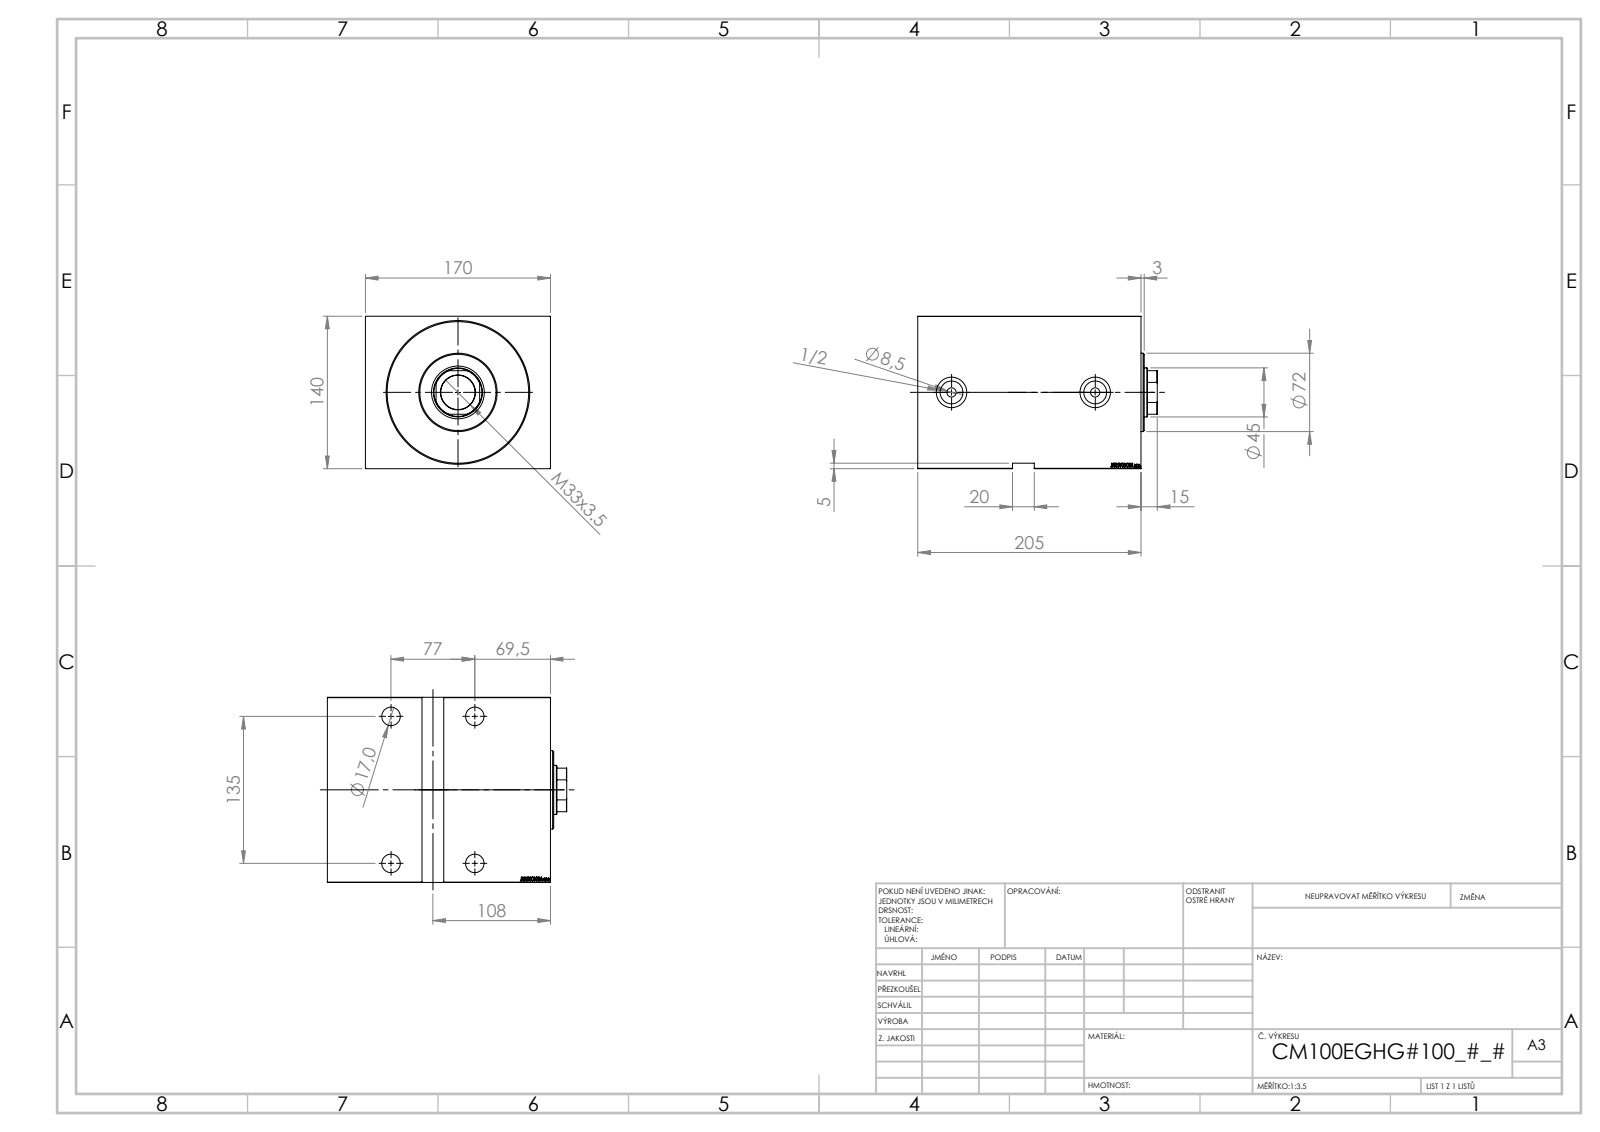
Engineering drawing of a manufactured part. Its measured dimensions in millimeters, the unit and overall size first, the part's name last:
Units: millimetres
Overall size (bounding box): 220 × 170 × 140
Round holes (diameter × count): ⌀17 ×4, ⌀25 ×4, ⌀8.5 ×2, ⌀20.96 ×2, ⌀28 ×2, ⌀31.5 ×1, ⌀45 ×1, ⌀48.5 ×1, ⌀100 ×1, ⌀130 ×1
Round bosses / shafts (diameter × count): ⌀102 ×1, ⌀72 ×1
Partial cylindrical surfaces — rounded edges, fillets, slot ends (radius × count): R22 ×1
Main face-to-face distances: 140, 170, 205, 26, 179, 5, 200, 174, 90, 188.4
Hole centre spacings: 77, 135, 155.42, 132
Volume: 4 074 000 mm³ · Surface area: 357 093 mm²
Bodies: 3 solids, 856 faces (410 planar, 52 cylindrical, 394 other)
Part name (STEP PRODUCT): V450CM_VC_B; V450CM_E_VCP; V450CM_E_Body
STEP written by: SolidWorks 2019 (CONFIG_CONTROL_DESIGN)
